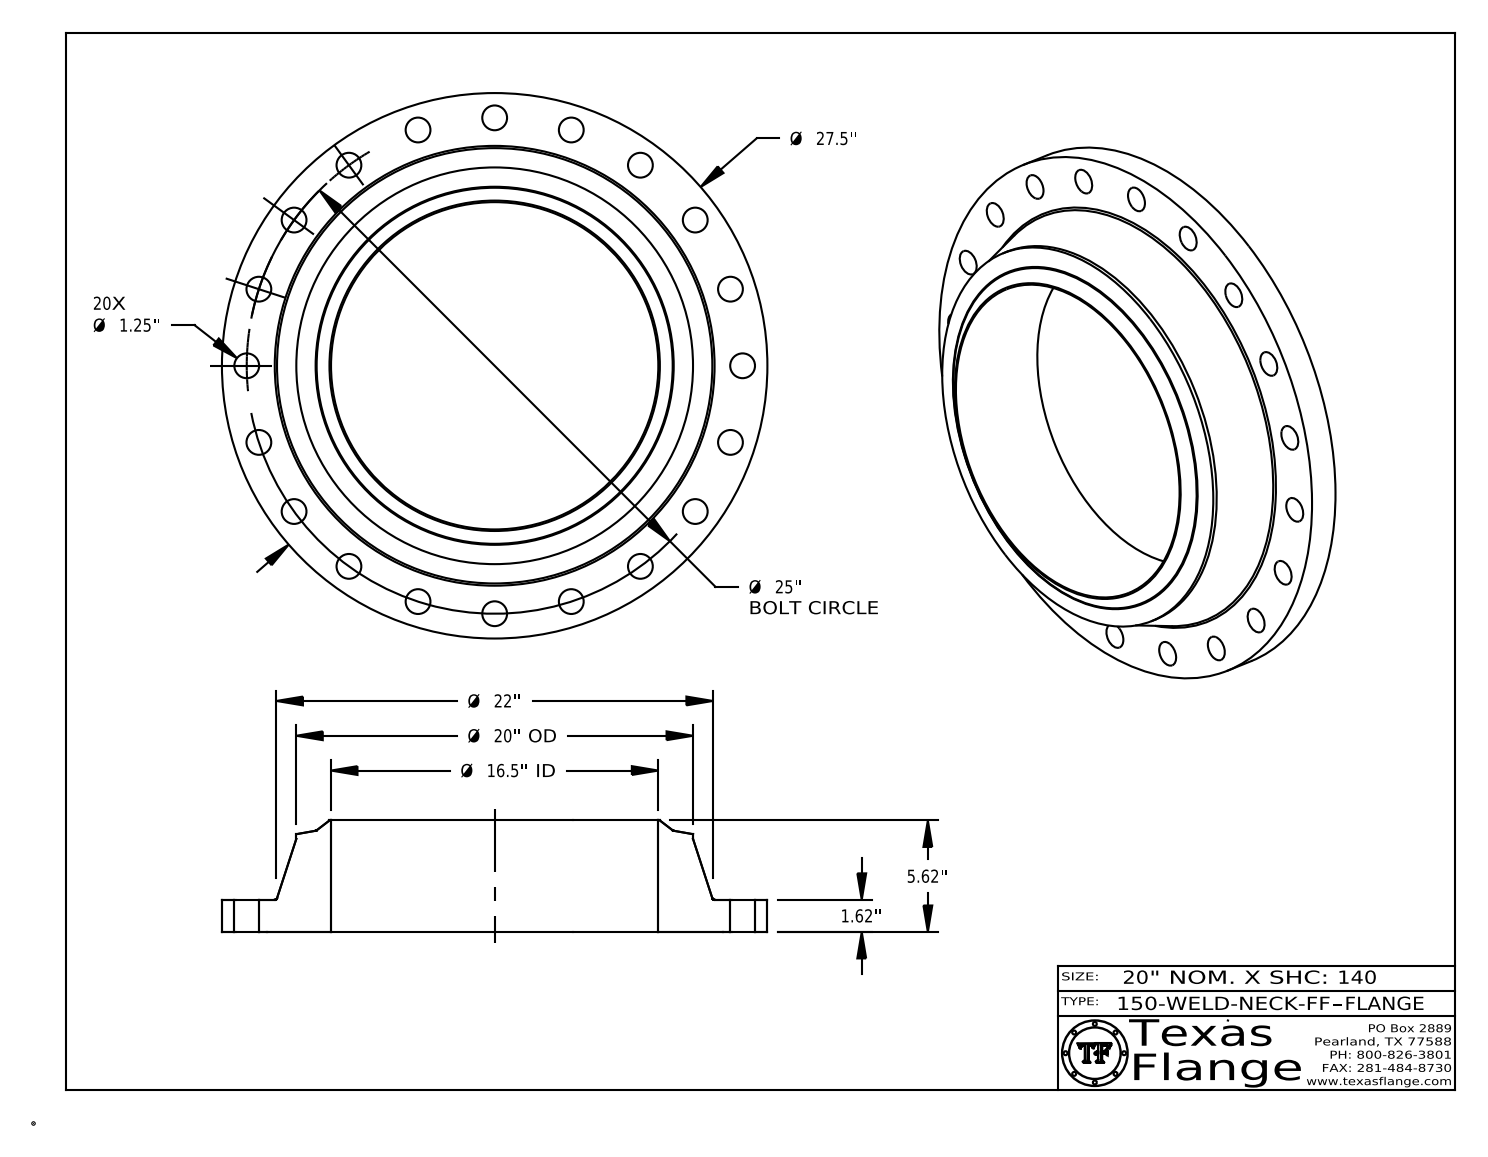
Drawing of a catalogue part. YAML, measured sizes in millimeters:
part_name: "150-WELD-NECK-FF"
step_written_by: "CATIA V5 STEP AP214 (AUTOMOTIVE_DESIGN)"
units: millimeters
bodies: {solids: 1, faces: 445, planar: 369, cylindrical: 66, other: 10}
overall_size: [698.5, 698.5, 142.7]
volume: 16910000
surface_area: 929700
round_holes:
  - {diameter: 31.8, count: 20}
  - {diameter: 12.6, count: 1}
  - {diameter: 419.1, count: 1}
round_bosses_or_shafts:
  - {diameter: 0.8, count: 8}
  - {diameter: 698.5, count: 1}
  - {diameter: 508, count: 1}
  - {diameter: 9.9, count: 1}
face_to_face_distances: [41.1, 142.7, 101.6, 40.8, 0.4, 102, 3.8, 3.7, 0.7, 2.4]
hole_center_spacings: [317.5, 373.2, 449, 513.7, 603.9, 627.2, 288.3, 565.8]
